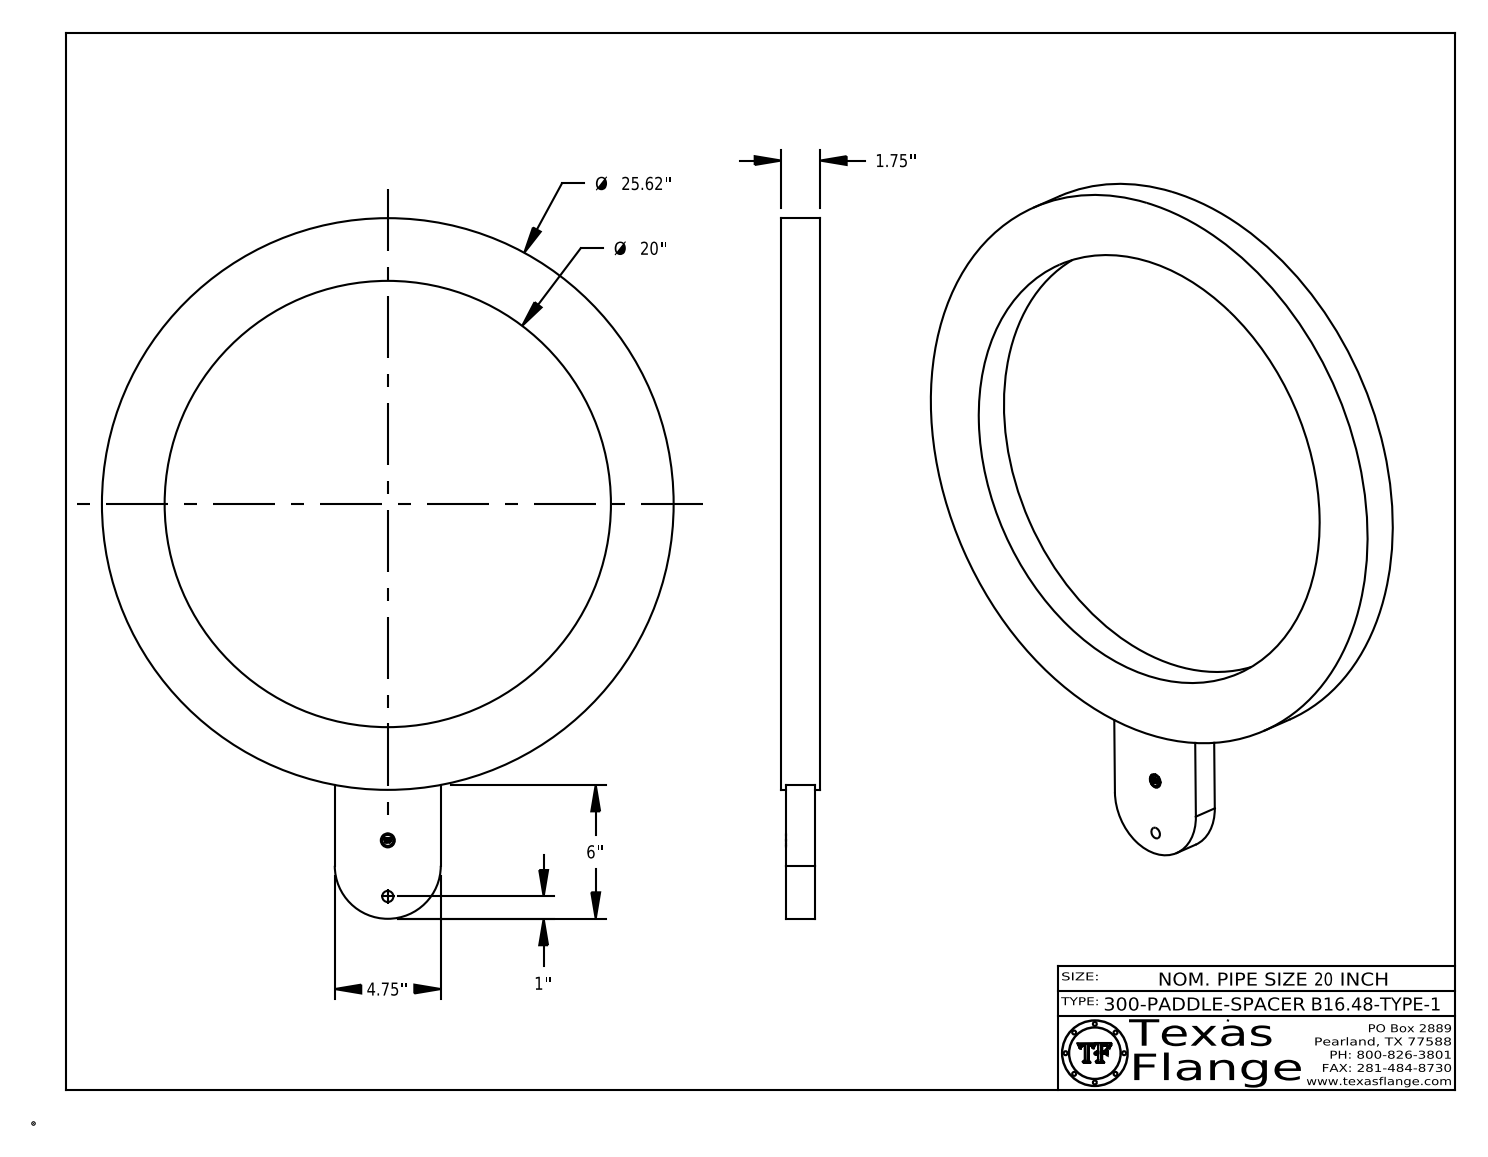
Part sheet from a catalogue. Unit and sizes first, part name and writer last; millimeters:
Units: millimetres
Overall size (bounding box): 797.5 × 650.7 × 44.5
Round holes (diameter × count): ⌀12.7 ×1, ⌀15.9 ×1, ⌀508 ×1
Round bosses / shafts (diameter × count): ⌀1 ×8, ⌀650.7 ×1, ⌀12.5 ×1
Partial cylindrical surfaces — rounded edges, fillets, slot ends (radius × count): R60.3 ×1
Main face-to-face distances: 44.5, 5.6, 38.9, 33.4, 120.7, 38.5, 33, 0.4, 5.9, 58.8
Hole centre spacings: 63.9, 382.9, 446.7
Volume: 6 316 000 mm³ · Surface area: 463 900 mm²
Bodies: 1 solid, 398 faces (371 planar, 27 cylindrical, 0 other)
Part name (STEP PRODUCT): 20-300-PADDLE-SPACER-B16.48-TYPE-2
STEP written by: CATIA V5 STEP AP214 (AUTOMOTIVE_DESIGN)
